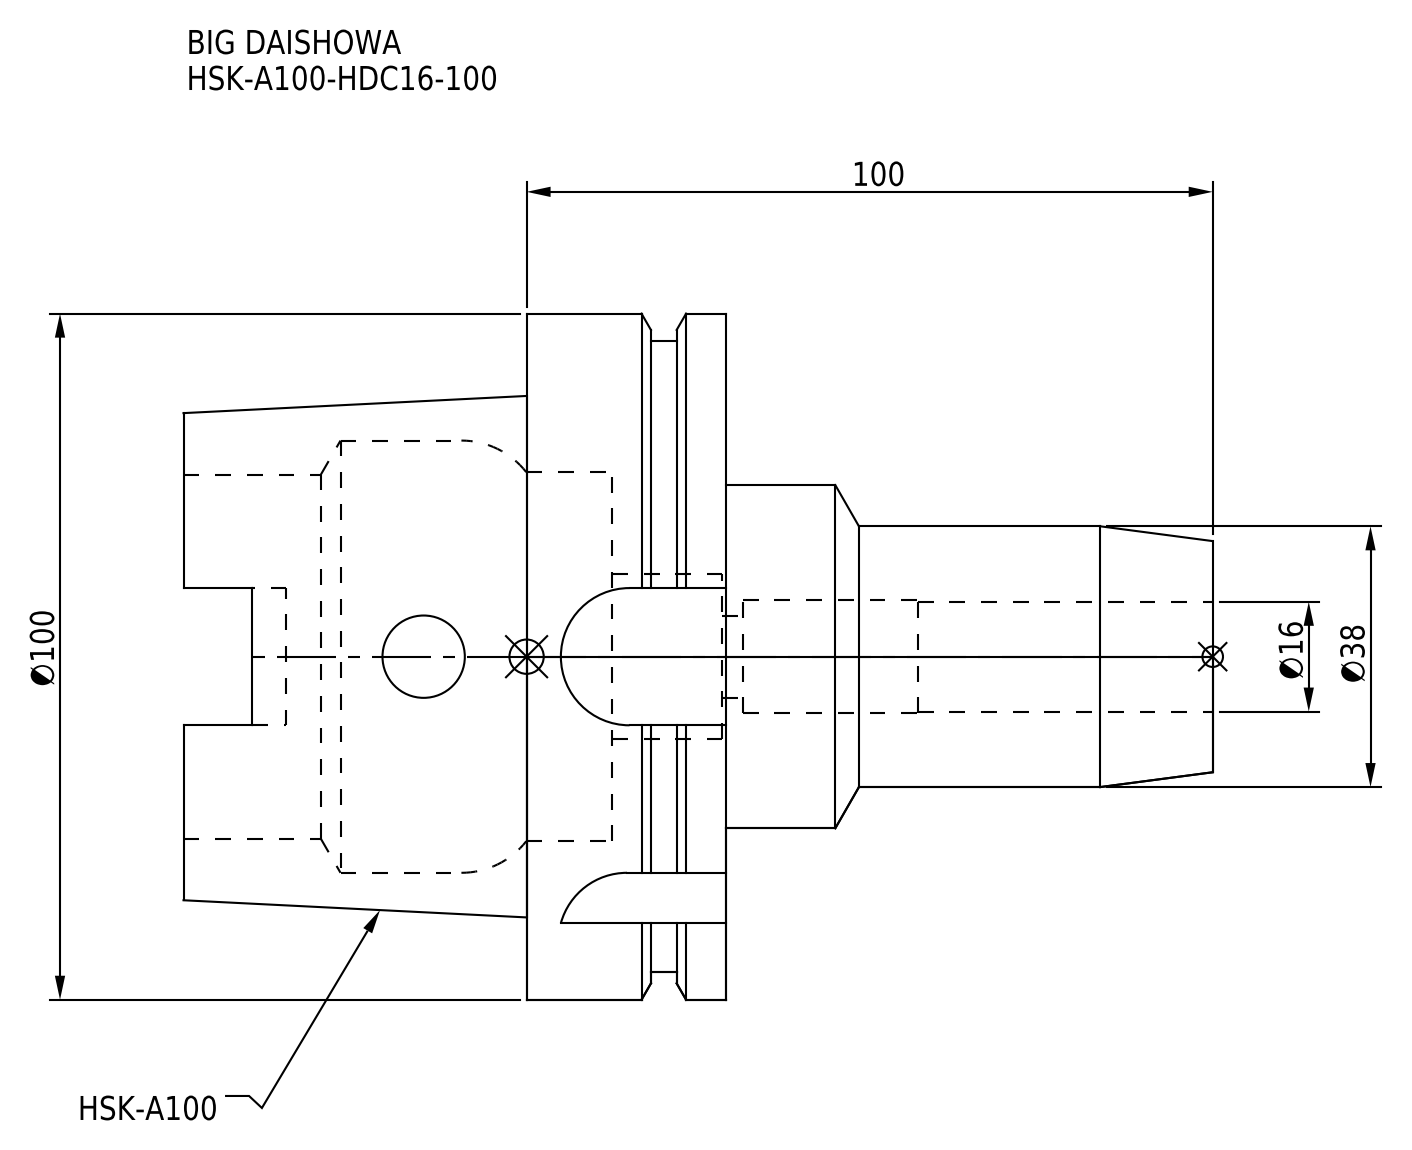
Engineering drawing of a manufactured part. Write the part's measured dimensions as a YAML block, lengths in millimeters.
part_name: "HSK-A100-HDC16-100"
step_written_by: "CREO PARAMETRIC BY PTC INC, 2016380 (AUTOMOTIVE_DESIGN)"
units: millimeters
bodies: {solids: 1, faces: 92, planar: 34, cylindrical: 40, other: 18}
overall_size: [150, 100, 100]
volume: 332181
surface_area: 61849
round_holes:
  - {diameter: 12, count: 2}
  - {diameter: 16, count: 1}
  - {diameter: 16.5, count: 1}
  - {diameter: 24, count: 1}
  - {diameter: 53, count: 1}
  - {diameter: 53.8, count: 1}
  - {diameter: 63, count: 1}
round_bosses_or_shafts:
  - {diameter: 100, count: 1}
  - {diameter: 92, count: 1}
  - {diameter: 50, count: 1}
  - {diameter: 38, count: 1}
partial_cylinders:
  - {radius: 4.88, count: 4}
  - {radius: 10, count: 4}
face_to_face_distances: [29, 16.55, 12.45, 79, 62.45, 50, 71, 87.55, 100, 150]
